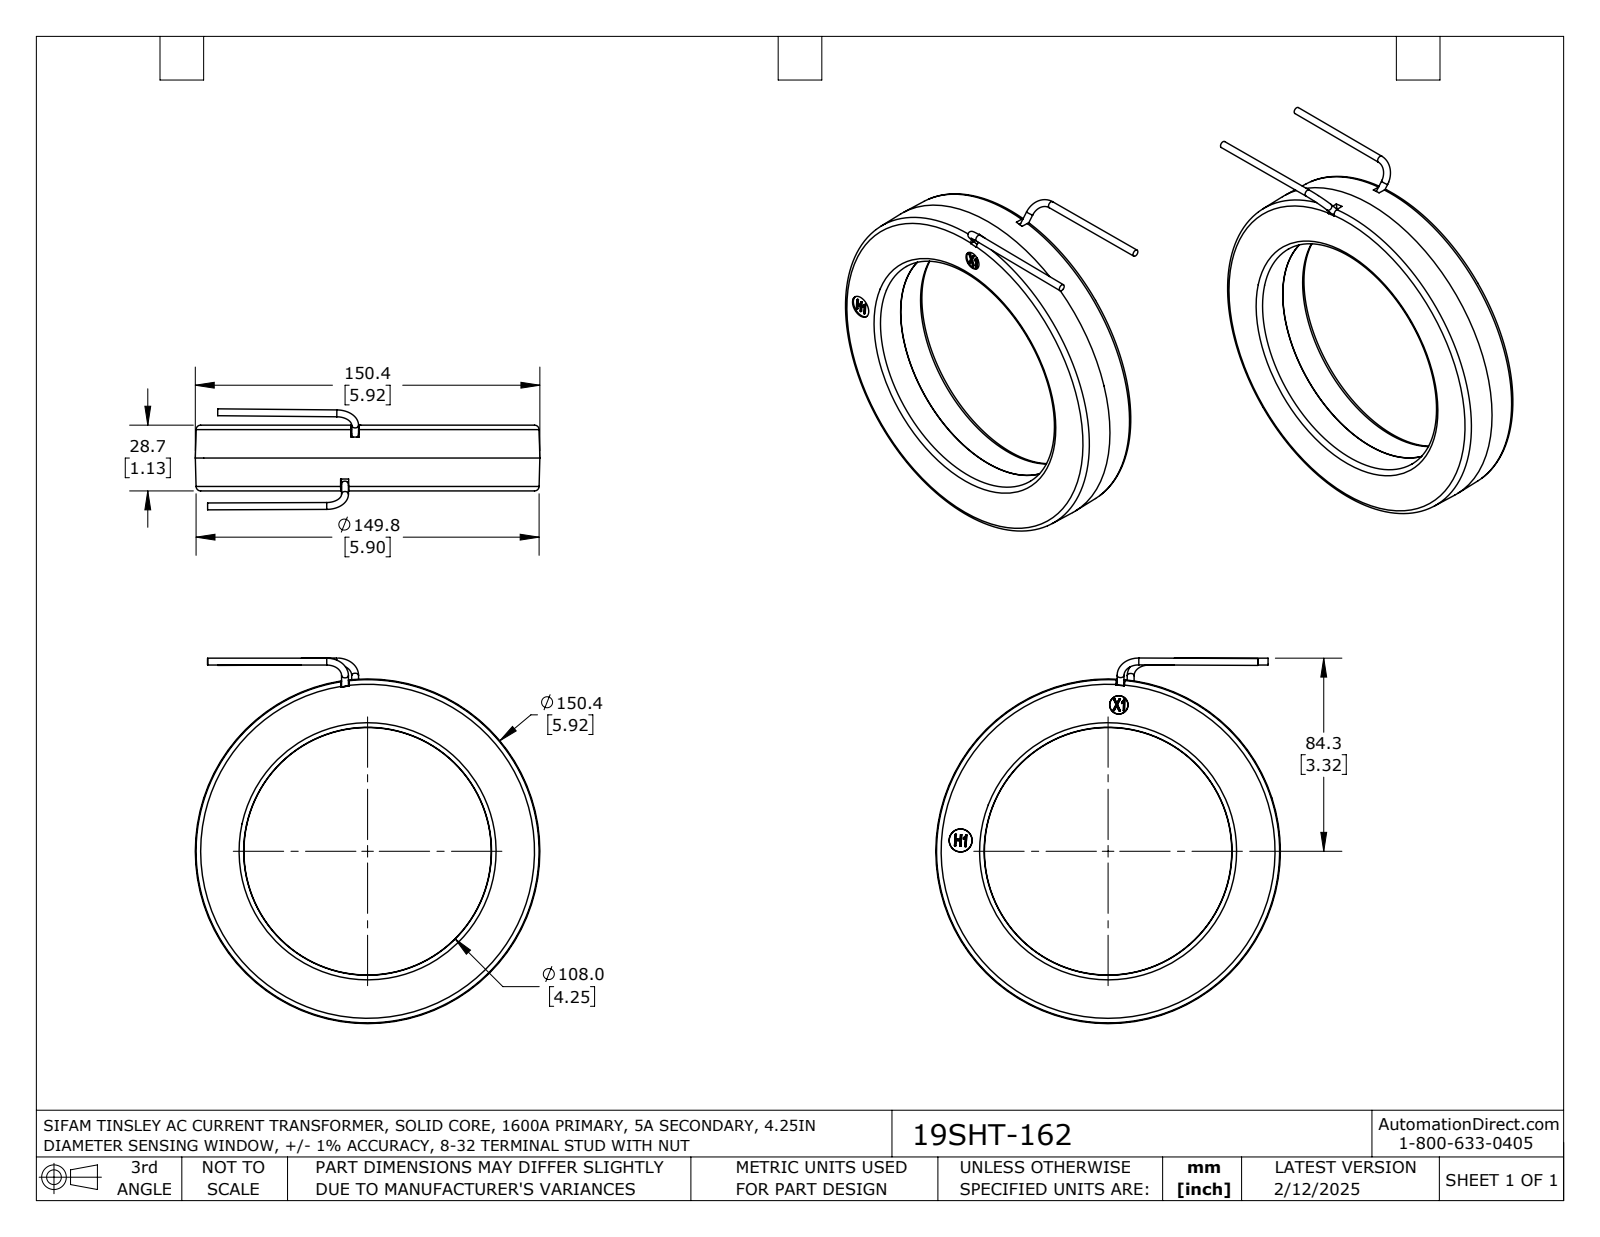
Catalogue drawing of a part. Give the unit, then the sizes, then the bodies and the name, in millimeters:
Units: millimetres
Overall size (bounding box): 167.9 × 152.4 × 73.9
Round bosses / shafts (diameter × count): ⌀10 ×2, ⌀6 ×2, ⌀5.5 ×2, ⌀4 ×2
Partial cylindrical surfaces — rounded edges, fillets, slot ends (radius × count): R2.8 ×12, R1 ×8, R2.5 ×8, R3.5 ×4, R0.3 ×2, R1.3 ×2, R1.4 ×2
Main face-to-face distances: 14.7, 14.6, 1, 29.2, 15.5, 15.6, 30.2, 152.4, 31.2, 156.7
Volume: 423 900 mm³ · Surface area: 105 000 mm²
Bodies: 1 solid, 412 faces (248 planar, 78 cylindrical, 86 other)
Part name (STEP PRODUCT): 19SHT-162
STEP written by: SolidWorks 2021 (AUTOMOTIVE_DESIGN)
